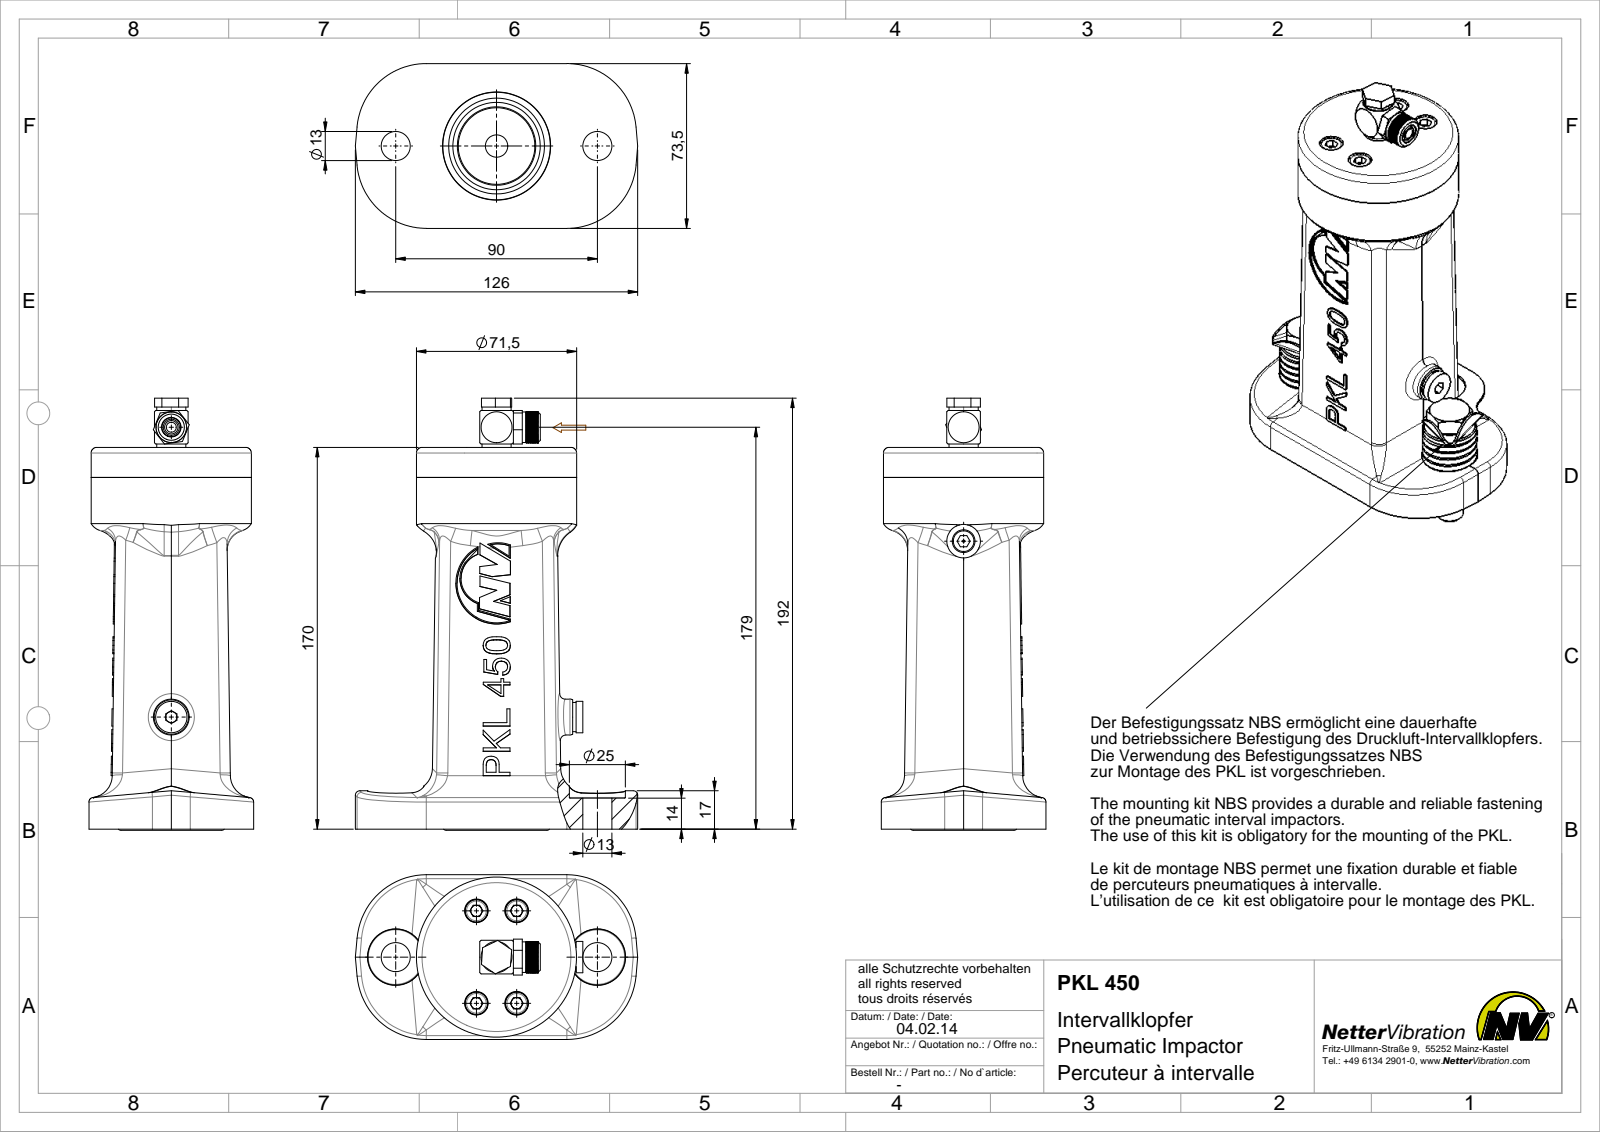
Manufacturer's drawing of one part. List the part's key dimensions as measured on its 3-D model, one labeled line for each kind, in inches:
Part name (STEP PRODUCT): PKL 450
STEP written by: SolidWorks 2015 (CONFIG_CONTROL_DESIGN)
Units: inches
Bodies: 19 solids, 2102 faces (550 planar, 512 cylindrical, 1040 other)
Overall size (bounding box): 8.406 × 4.961 × 2.894
Volume: 38.27 in³ · Surface area: 161 in²
Round holes (diameter × count): ⌀0.197 ×4, ⌀0.256 ×4, ⌀0.287 ×4, ⌀0.413 ×4, ⌀0.337 ×3, ⌀0.177 ×2, ⌀0.394 ×2, ⌀0.492 ×2, ⌀0.512 ×2, ⌀0.528 ×2, ⌀0.984 ×2, ⌀0.039 ×1
Round bosses / shafts (diameter × count): ⌀0.394 ×5, ⌀0.402 ×4, ⌀0.343 ×4, ⌀0.236 ×4, ⌀0.957 ×2, ⌀0.945 ×2, ⌀0.709 ×2, ⌀0.512 ×2
Partial cylindrical surfaces — rounded edges, fillets, slot ends (radius × count): R0.079 ×10, R0.394 ×8, R0.551 ×5, R0.039 ×4, R0.197 ×4, R1.22 ×4, R0.709 ×3, R0.472 ×2
Main face-to-face distances: 6.706, 0.984, 5.722, 0.039, 5.726, 0.98, 6.178, 0.457, 0.453, 0.528
Hole centre spacings: 0.886, 1.633, 1.772, 2.276, 0.709, 1.624, 2.001, 3.09
